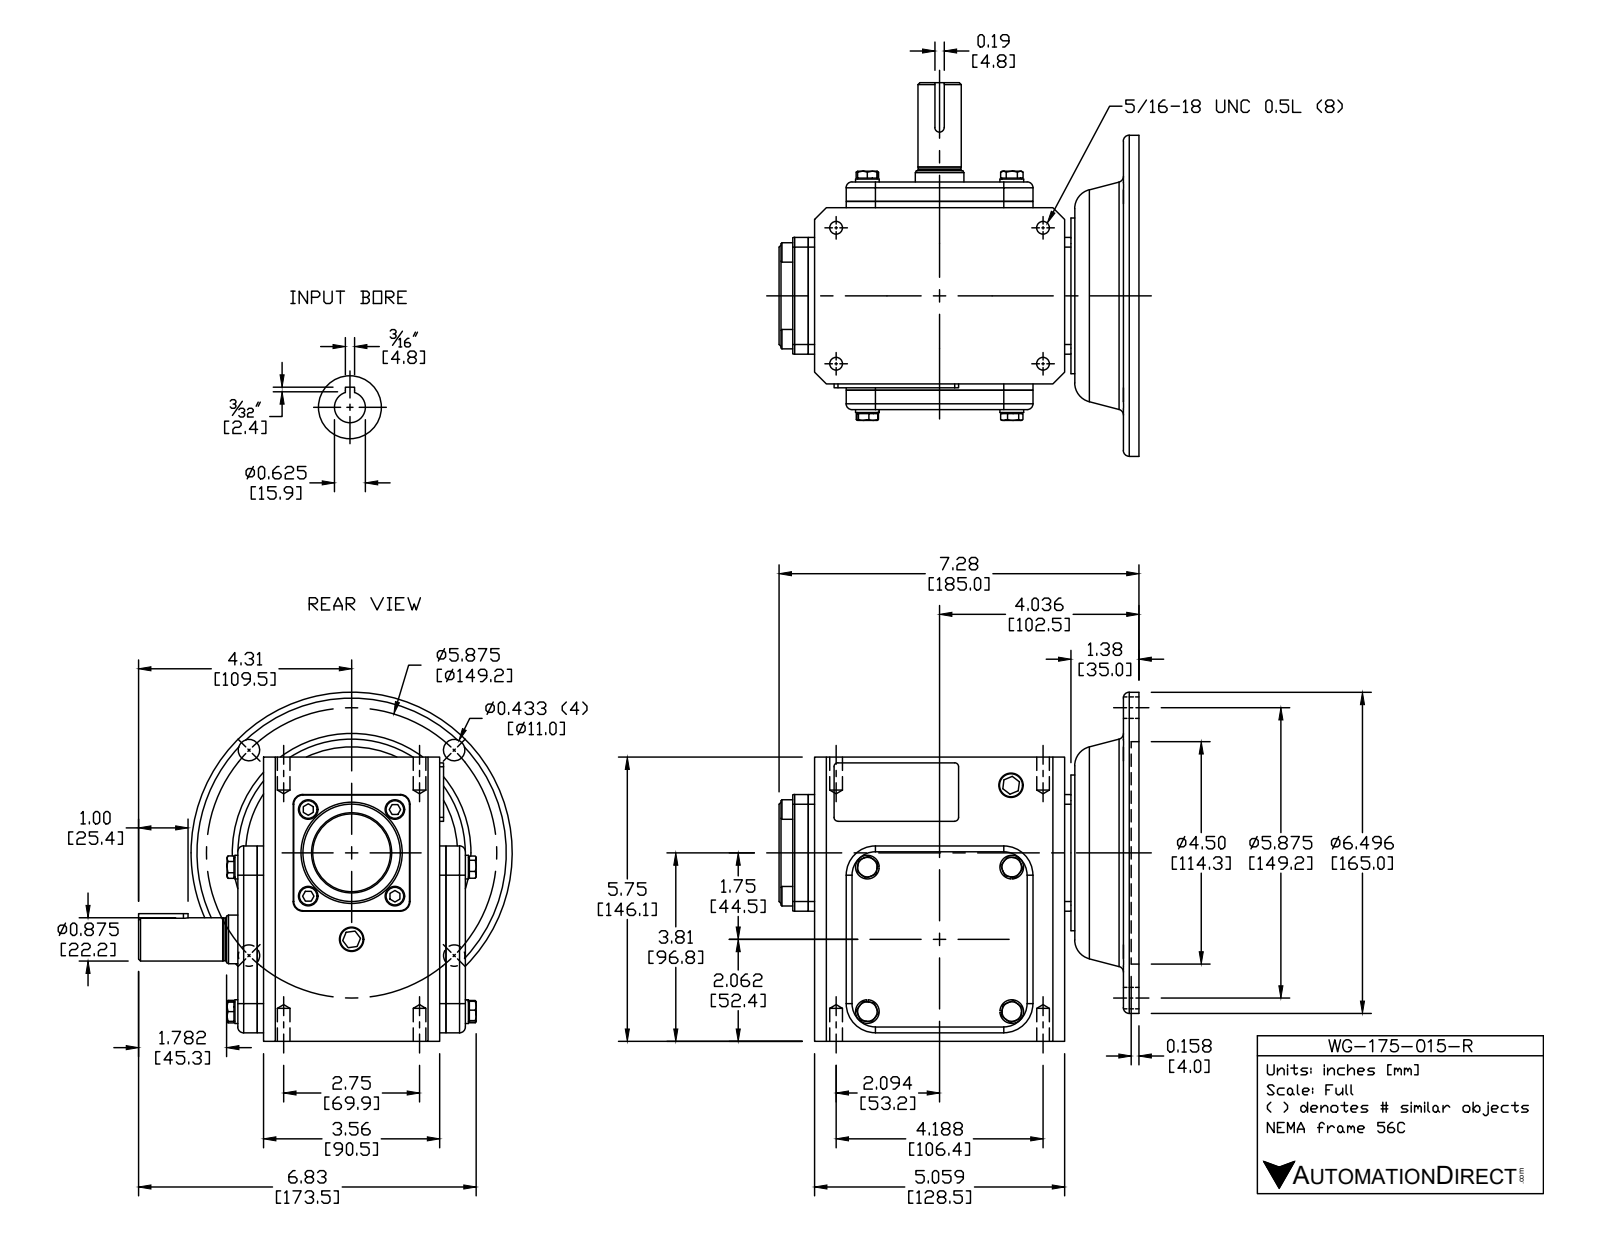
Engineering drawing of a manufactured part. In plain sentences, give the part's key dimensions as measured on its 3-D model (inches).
The part is named "WG-175-015-R". Its 3-D file was written by "SolidWorks 2015 (CONFIG_CONTROL_DESIGN)". It is 43 solids with 613 faces: 312 planar, 172 cylindrical and 129 other. Overall it measures 7.559 by 7.283 by 7.06 inches. Its volume is 131.9 cubic inches and its surface area 366.4 square inches. Round holes: 4 of diameter 0.257, 4 of diameter 0.406, 1 of diameter 0.512, 1 of diameter 0.625, 1 of diameter 0.984, 1 of diameter 1.181, 1 of diameter 1.457, 1 of diameter 1.575, 1 of diameter 3.543, 1 of diameter 4.5. Round bosses or shafts: 8 of diameter 0.394, 4 of diameter 0.48, 2 of diameter 0.512, 1 of diameter 6.496, 1 of diameter 3.15, 1 of diameter 2.047, 1 of diameter 1.575, 1 of diameter 0.875. Partial cylindrical surfaces (rounded edges, fillets, slot ends): 8 of radius 0.079, 8 of radius 0.118, 4 of radius 0.197, 4 of radius 0.591, 2 of radius 0.02, 2 of radius 0.039, 1 of radius 0.094. The main face-to-face distances are 0.128, 3.819, 4.213, 0.394, 4.085, 3.691, 0.522, 0.315, 5.75, 6.693. The hole center spacings are 2.937, 4.154, 2.103, 2.75, 4.188, 4.354, 5.01, 5.875.
